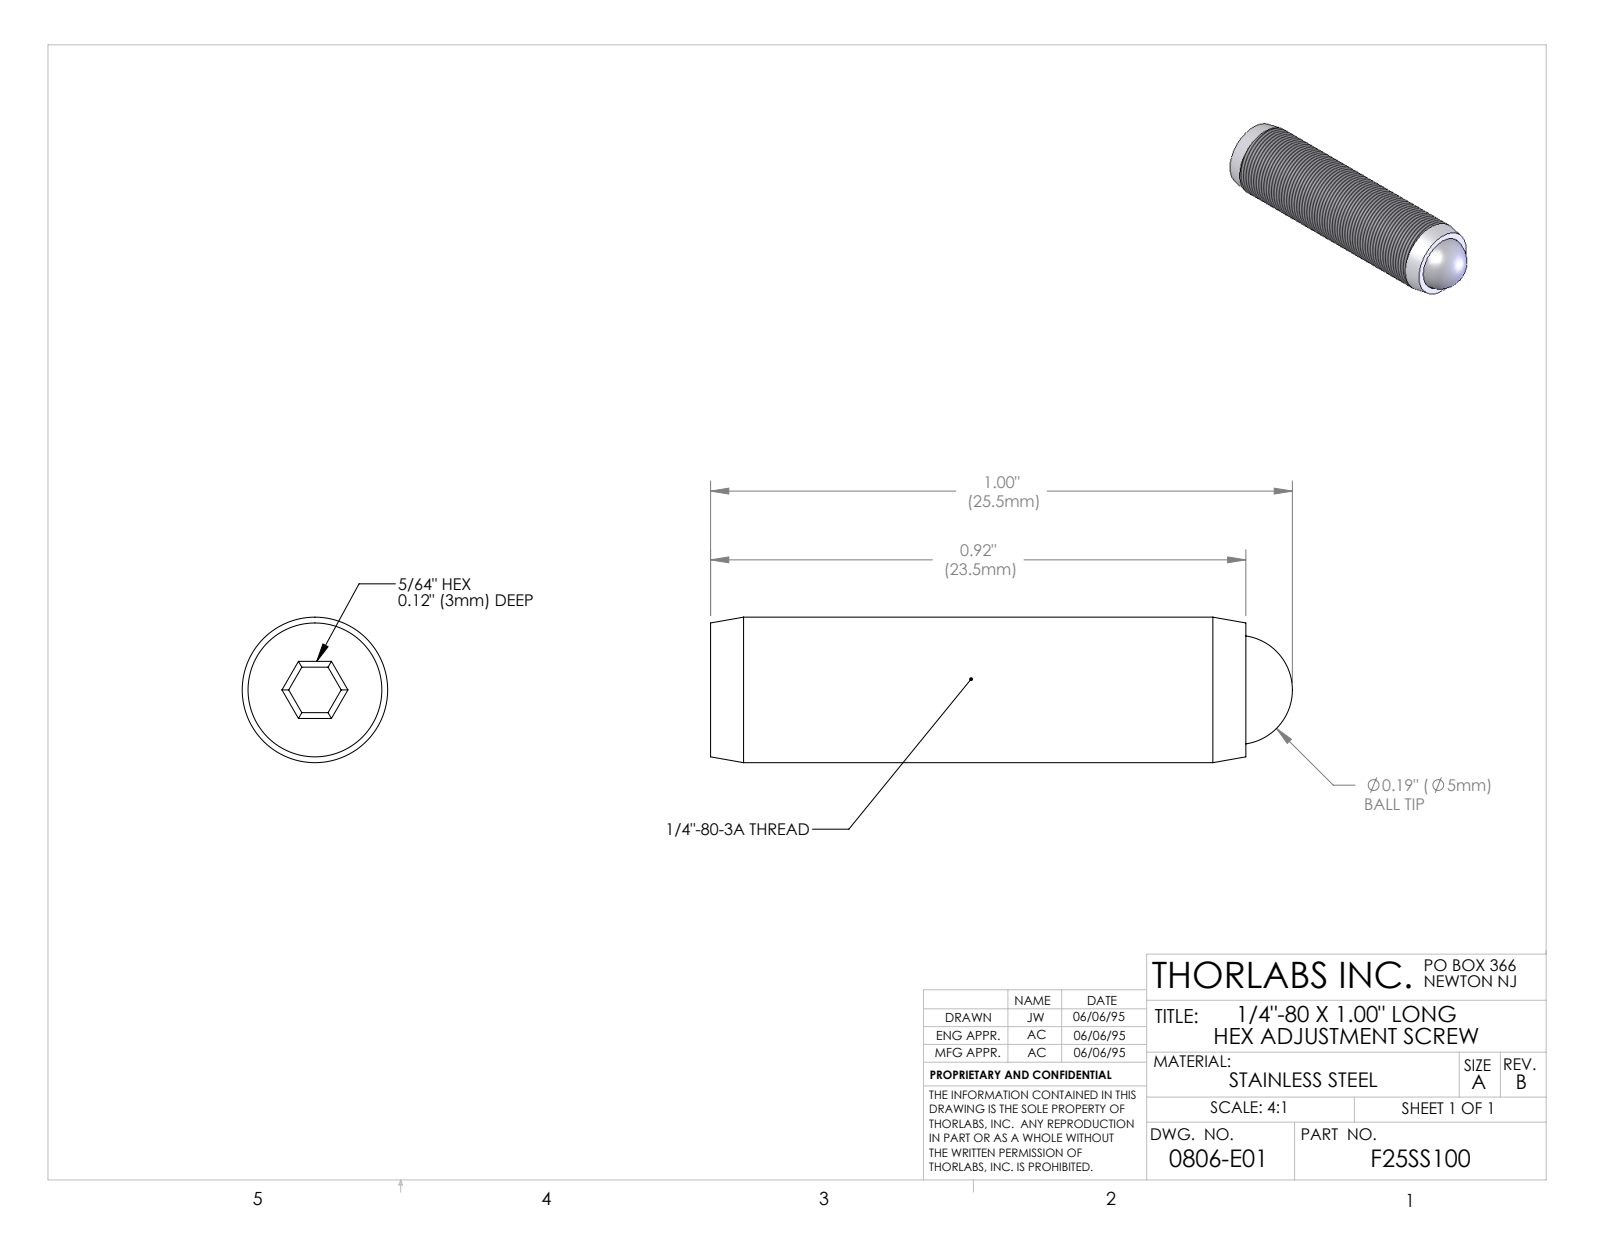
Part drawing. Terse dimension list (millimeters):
name: 0806-E0W
written by: SolidWorks 2007 (AUTOMOTIVE_DESIGN)
unit: mm
bodies: 2 solids, 29 faces (15 planar, 4 cylindrical, 10 other)
size: 25.4 × 6.35 × 6.35
volume: 741 mm³; area: 637 mm²
holes: 1× ⌀4.78
bosses: 1× ⌀6.35
face distances: 23.37, 1.99, 3.05, 20.32, 1.98
